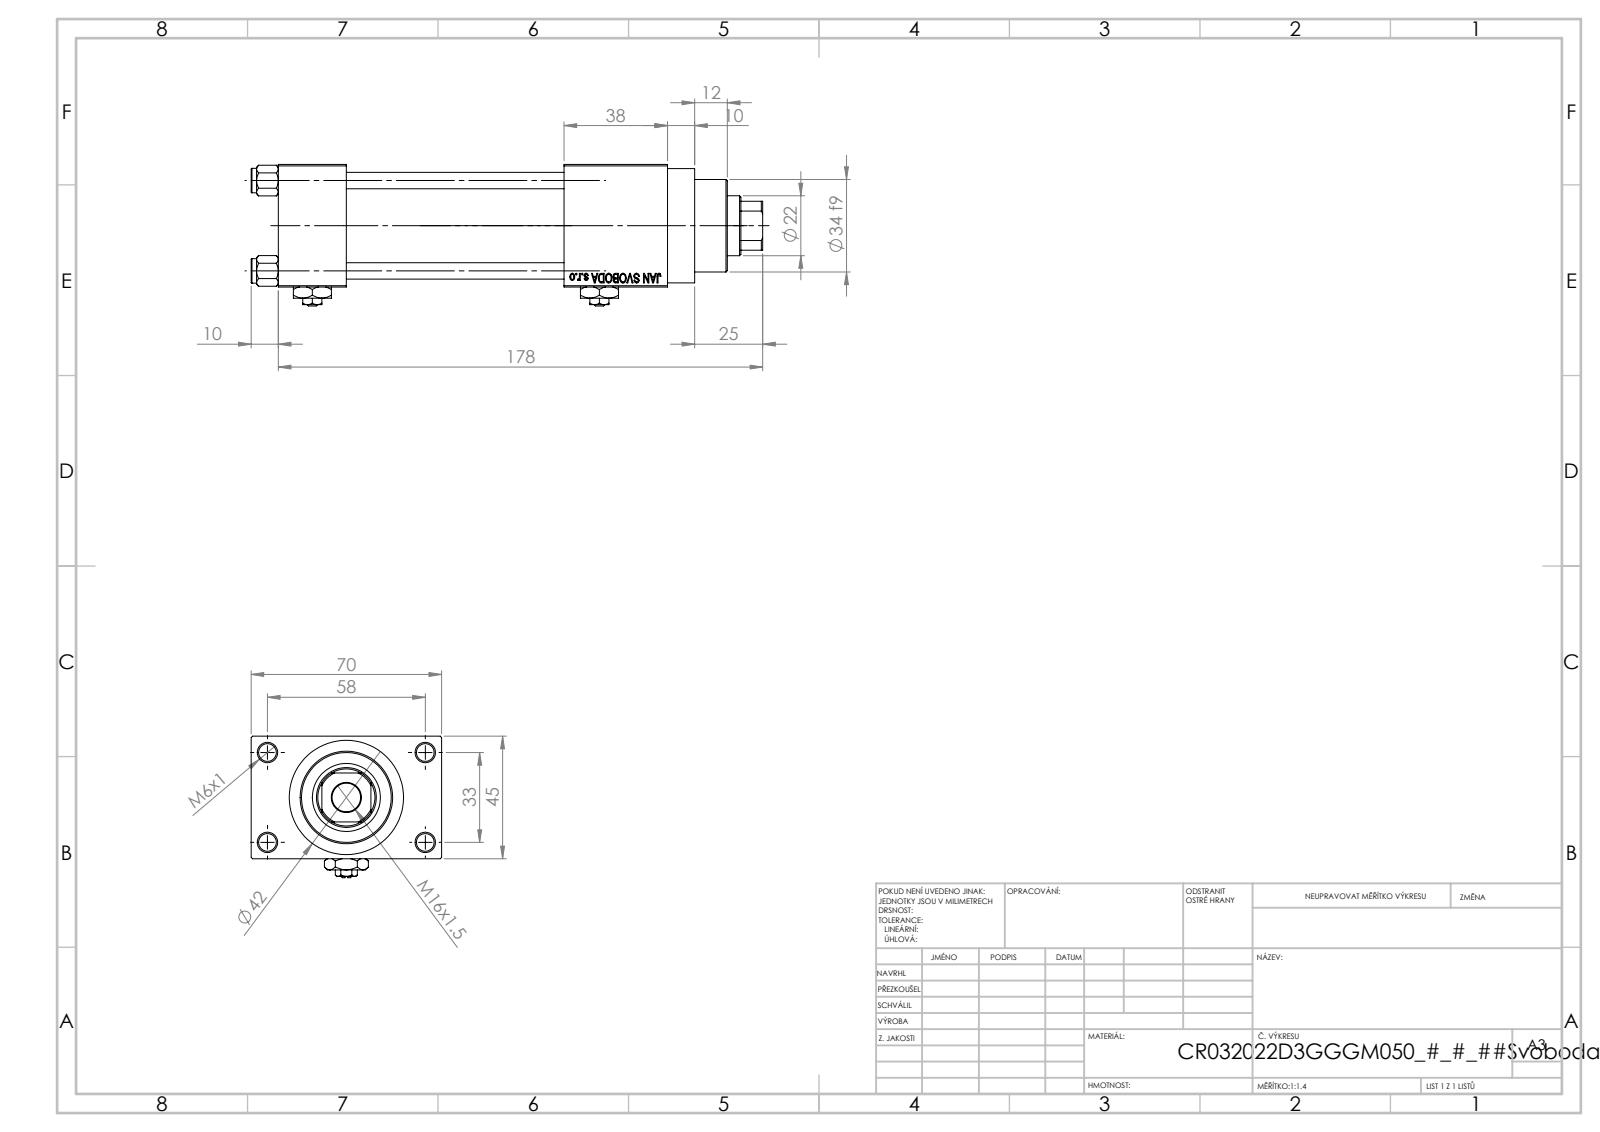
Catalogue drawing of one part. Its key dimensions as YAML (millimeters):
part_name: "Zatka_pro_OIL_PORT; V215CR_D_TYCINKA; V215_VC_A; NUT_M5_D (+2 more)"
step_written_by: "SolidWorks 2019 (CONFIG_CONTROL_DESIGN)"
units: millimeters
bodies: {solids: 13, faces: 1202, planar: 542, cylindrical: 100, other: 560}
overall_size: [188, 70, 52]
volume: 268060
surface_area: 92133
round_holes:
  - {diameter: 6, count: 4}
  - {diameter: 6.5, count: 4}
  - {diameter: 7, count: 2}
  - {diameter: 13.16, count: 2}
  - {diameter: 20, count: 2}
  - {diameter: 10.5, count: 1}
  - {diameter: 22, count: 1}
  - {diameter: 24, count: 1}
  - {diameter: 25, count: 1}
  - {diameter: 32, count: 1}
  - {diameter: 33, count: 1}
round_bosses_or_shafts:
  - {diameter: 9, count: 4}
  - {diameter: 42, count: 1}
  - {diameter: 38, count: 1}
  - {diameter: 34, count: 1}
partial_cylinders:
  - {radius: 10.5, count: 1}
face_to_face_distances: [45, 25, 12.5, 57.5, 80, 105, 118, 70, 38, 143]
hole_center_spacings: [12.4, 23.48, 33.2, 33.37, 35.35, 45.6, 56.35, 33]
